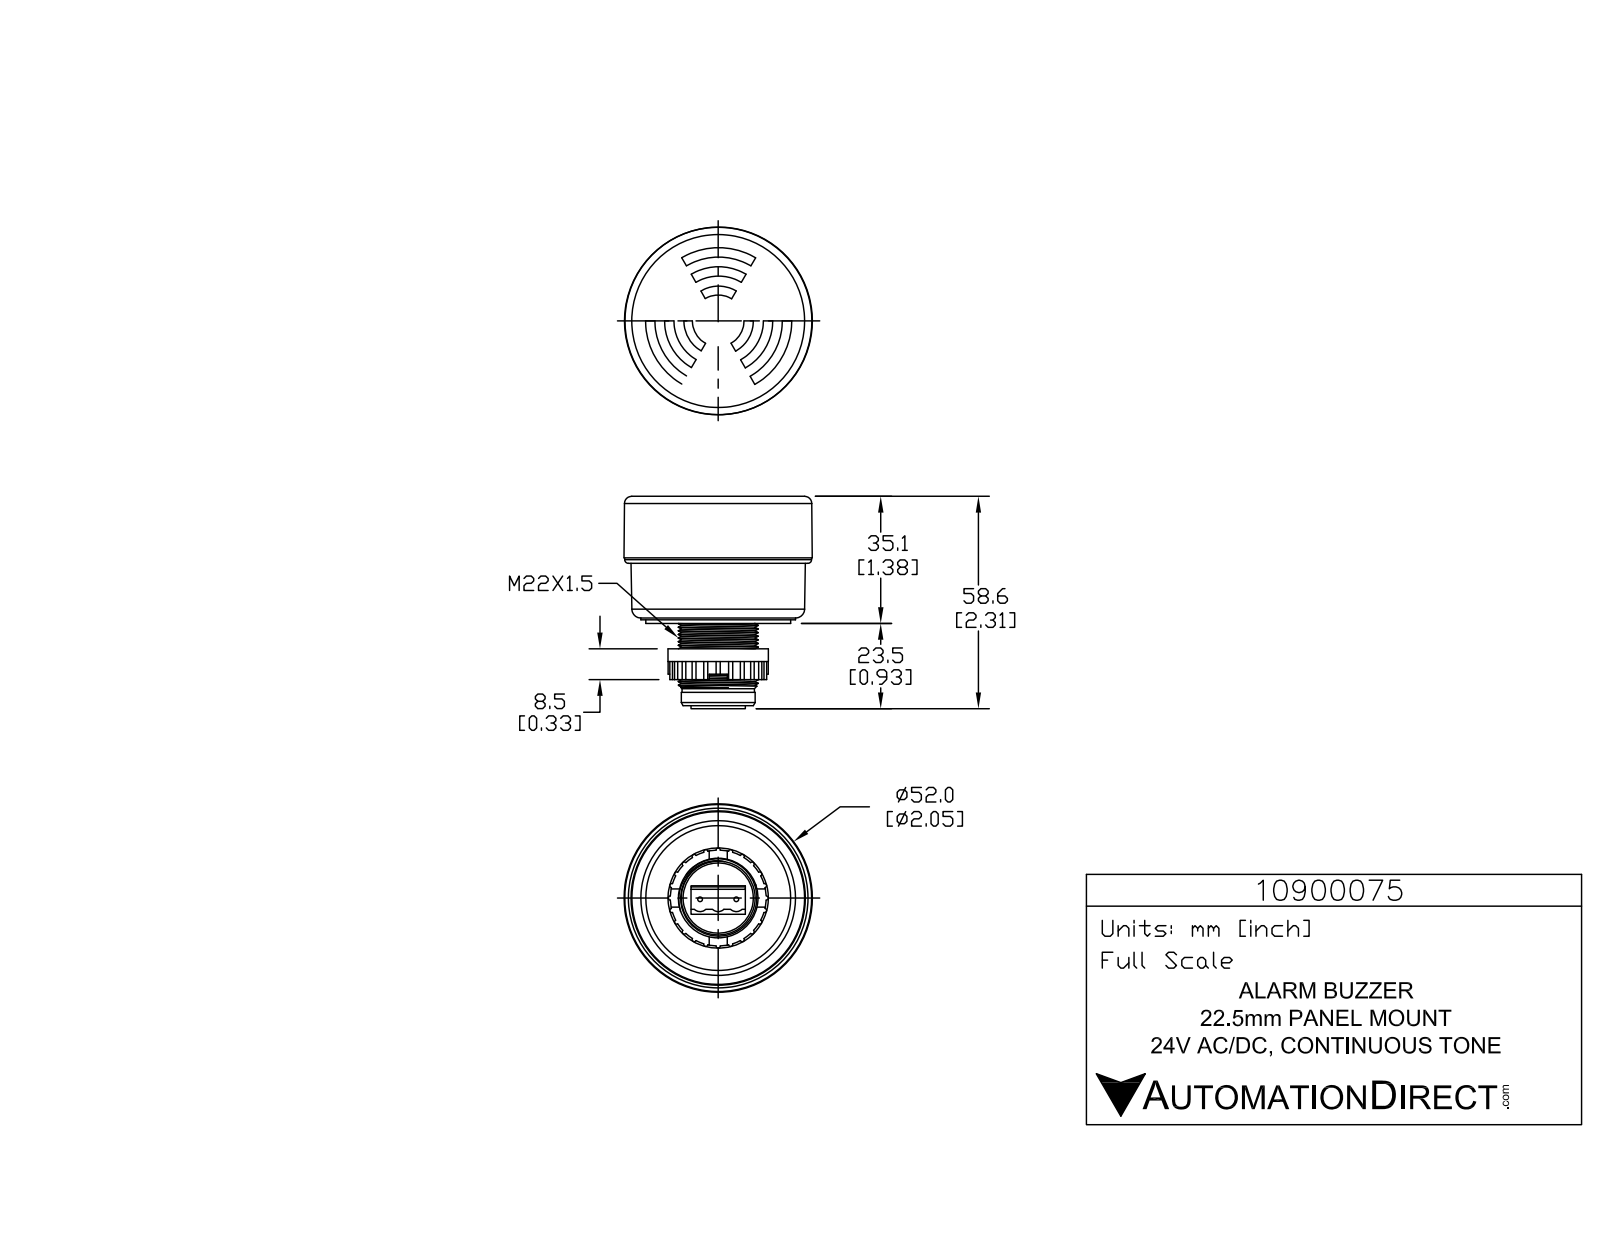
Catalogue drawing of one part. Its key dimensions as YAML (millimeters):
part_name: "10900075"
step_written_by: "SolidWorks 2017 (AUTOMOTIVE_DESIGN)"
units: millimeters
bodies: {solids: 1, faces: 1180, planar: 766, cylindrical: 311, other: 103}
overall_size: [58.6, 52.2, 52.1]
volume: 76300
surface_area: 14710
round_holes:
  - {diameter: 1, count: 4}
  - {diameter: 23, count: 1}
round_bosses_or_shafts:
  - {diameter: 5.7, count: 4}
  - {diameter: 1.4, count: 4}
  - {diameter: 1.3, count: 2}
  - {diameter: 51.6, count: 1}
  - {diameter: 42.7, count: 1}
  - {diameter: 40, count: 1}
  - {diameter: 27.7, count: 1}
  - {diameter: 22, count: 1}
partial_cylinders:
  - {radius: 0.6, count: 24}
  - {radius: 0.2, count: 8}
  - {radius: 0.2, count: 8}
  - {radius: 0.2, count: 8}
  - {radius: 3.3, count: 8}
  - {radius: 0.1, count: 4}
  - {radius: 0.1, count: 4}
  - {radius: 0.2, count: 4}
face_to_face_distances: [34.9, 7, 41.9, 1, 8, 33.9, 22.8, 23.8, 15.8, 57.7]
hole_center_spacings: [6.1]
